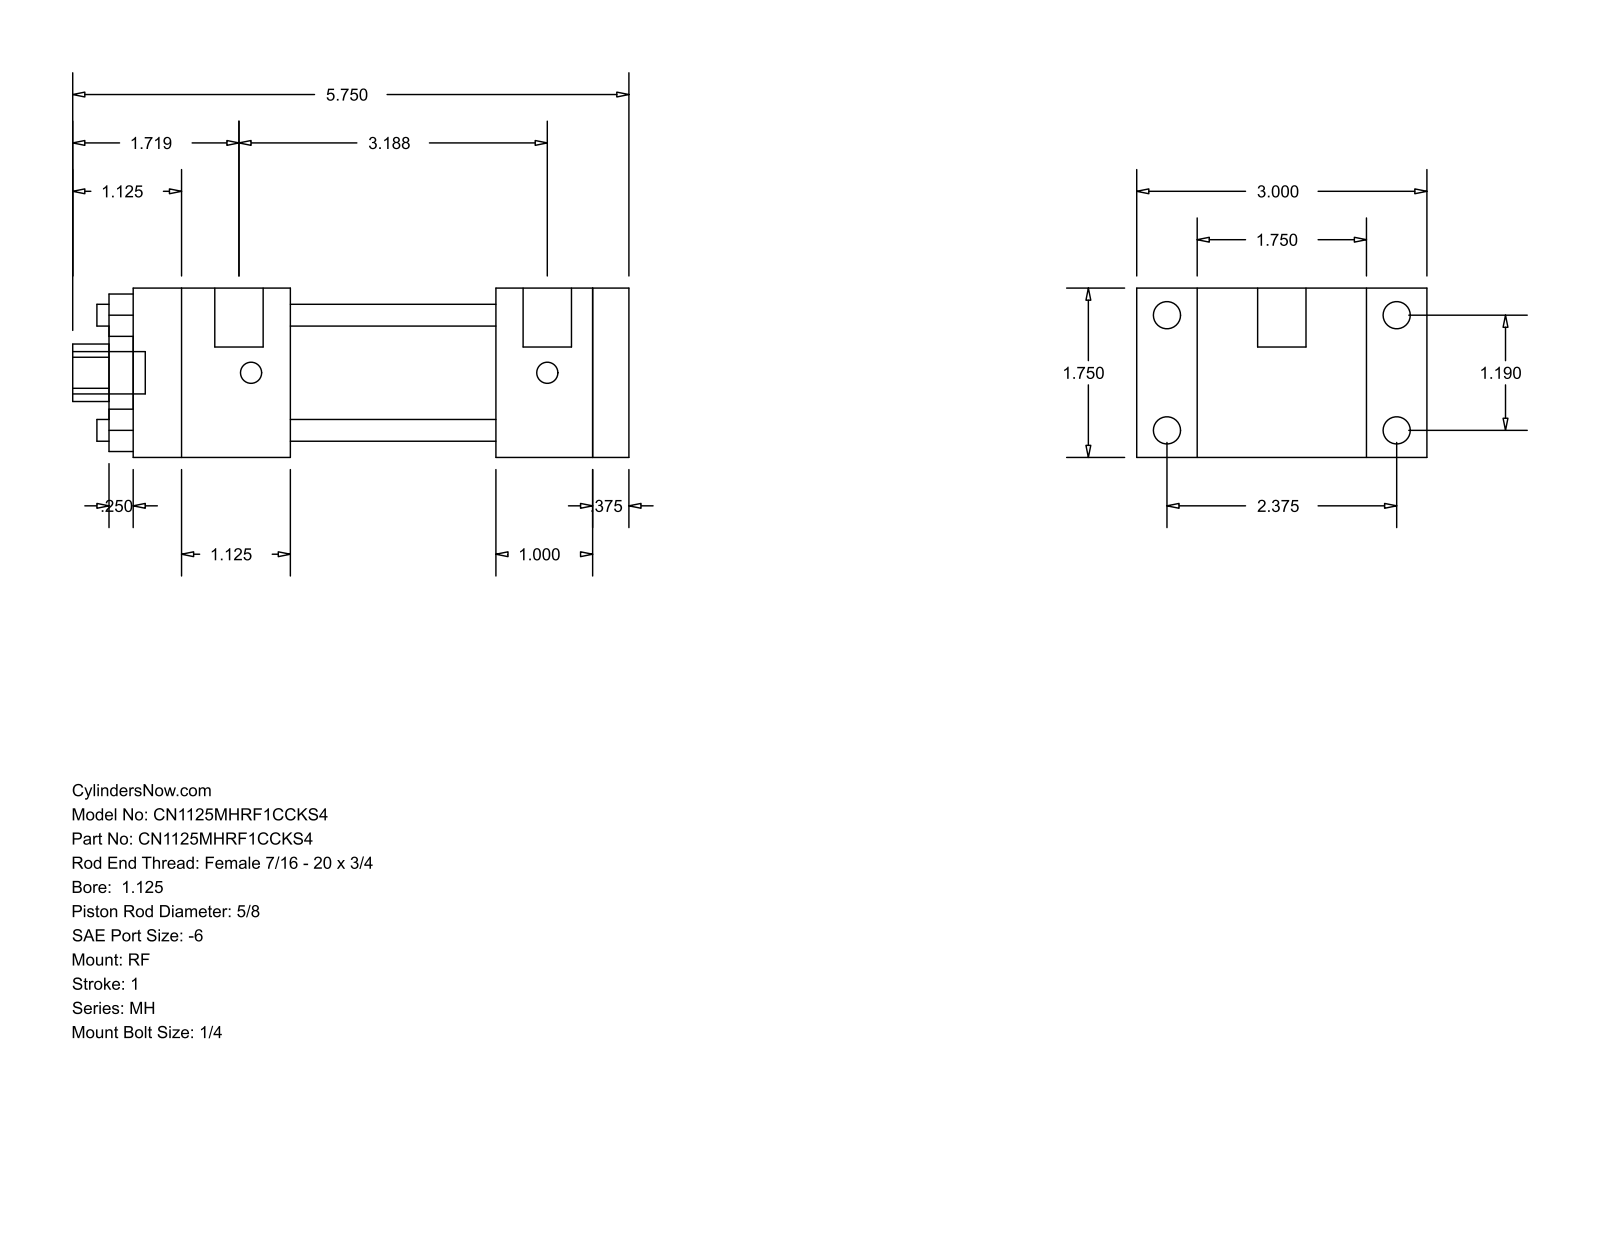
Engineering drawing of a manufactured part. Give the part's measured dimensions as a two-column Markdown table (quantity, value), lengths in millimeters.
| quantity | value |
| --- | --- |
| part name | MH_RF__0112_0.625 |
| STEP written by | GSSL Pune (CONFIG_CONTROL_DESIGN) |
| units | millimeters |
| bodies | 0 solids, 92 faces (64 planar, 28 cylindrical, 0 other) |
| overall size | 146.05 × 76.2 × 44.45 |
| round holes (diameter × count) | 5.71 × 4, 15.88 × 1, 28.57 × 1, 34.92 × 1 |
| round bosses / shafts (diameter × count) | 7.14 × 4, 5.56 × 4, 12.7 × 2, 11.11 × 1 |
| partial cylindrical surfaces (radius × count) | 7.54 × 1 |
| main face-to-face distances | 44.46, 9.52, 15.87, 79.38, 88.9, 53.97, 25.41, 34.93, 41.27, 95.24 |
| hole center spacings | 21.37, 30.22, 42.74 |
